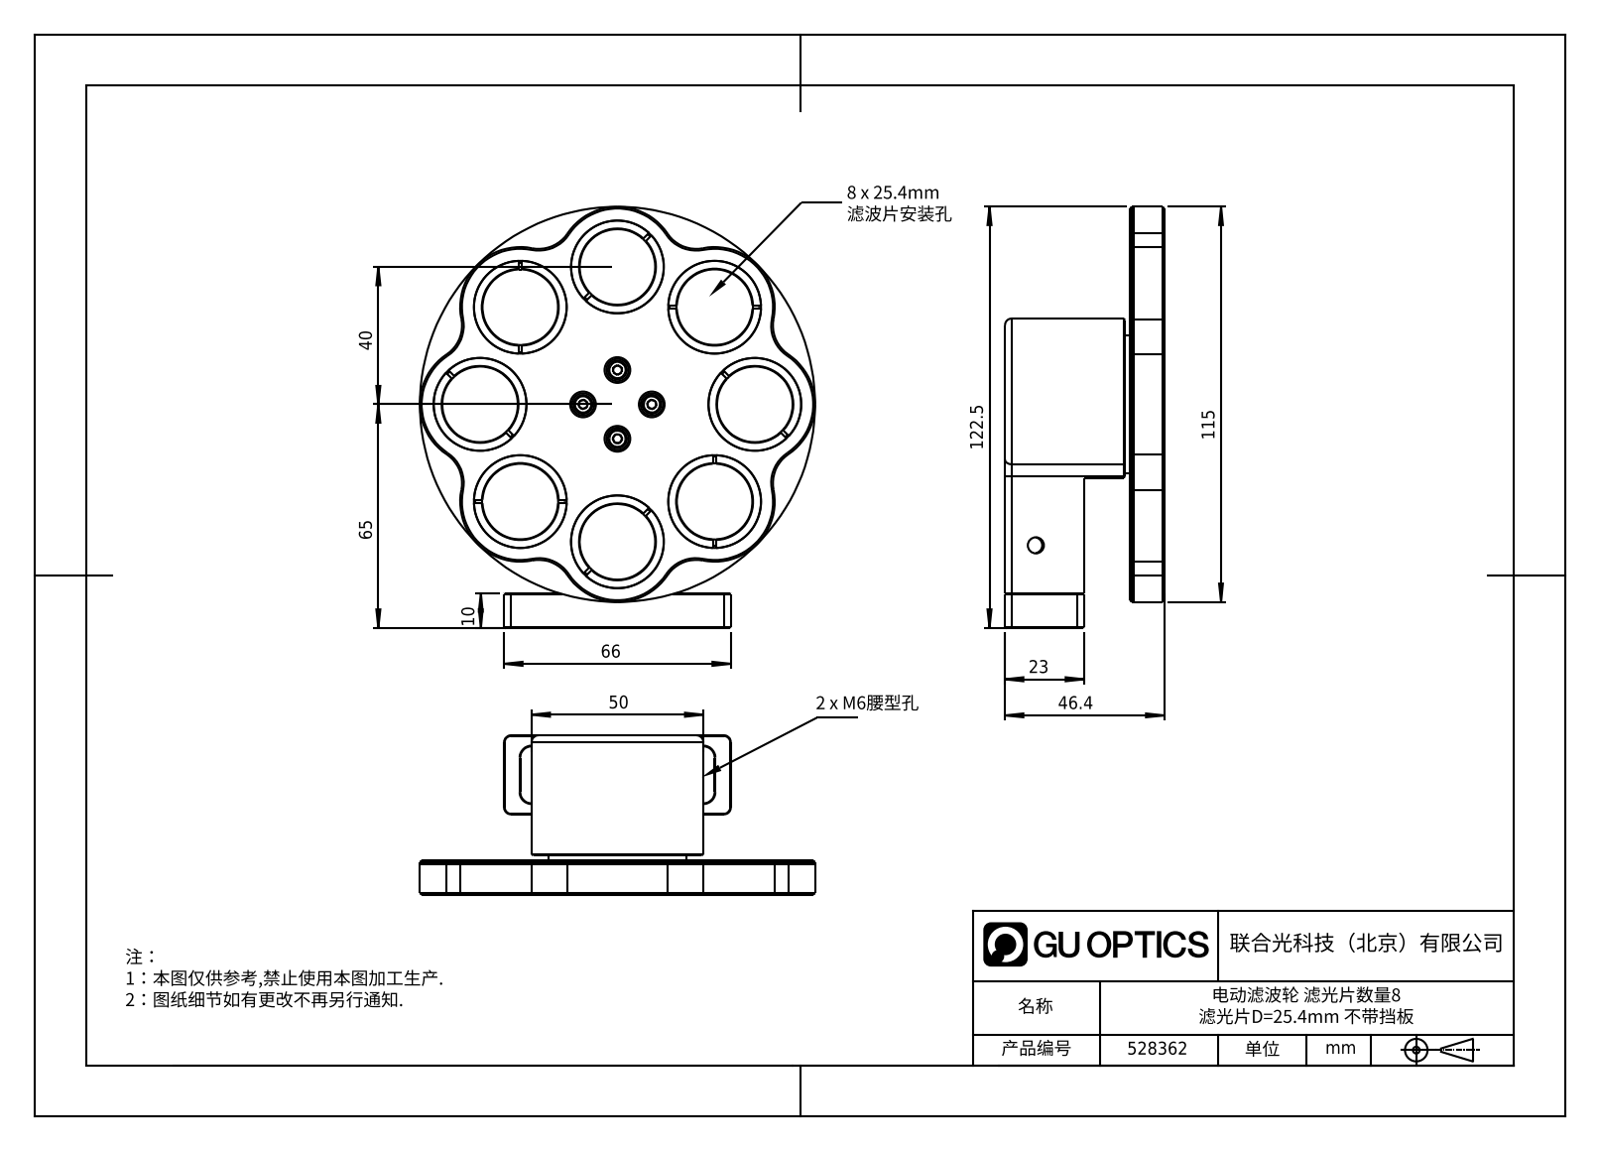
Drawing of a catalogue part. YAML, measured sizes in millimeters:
part_name: "528362"
step_written_by: "SolidWorks 2020 (CONFIG_CONTROL_DESIGN)"
units: millimeters
bodies: {solids: 0, faces: 464, planar: 263, cylindrical: 102, other: 99}
overall_size: [122.5, 115, 46.4]
round_holes:
  - {diameter: 27, count: 6}
  - {diameter: 8, count: 4}
  - {diameter: 4.7, count: 1}
  - {diameter: 115, count: 1}
round_bosses_or_shafts:
  - {diameter: 26, count: 8}
  - {diameter: 23, count: 8}
  - {diameter: 22, count: 8}
  - {diameter: 6.5, count: 4}
  - {diameter: 5.5, count: 4}
  - {diameter: 5.2, count: 4}
  - {diameter: 7, count: 2}
  - {diameter: 3.5, count: 2}
partial_cylinders:
  - {radius: 0.3, count: 20}
  - {radius: 10, count: 8}
  - {radius: 17.5, count: 8}
  - {radius: 2, count: 6}
  - {radius: 3.3, count: 4}
  - {radius: 5, count: 2}
  - {radius: 25, count: 1}
face_to_face_distances: [10, 1, 9, 6, 5, 4, 36.4, 37.4, 42.4, 46.4]
hole_center_spacings: [40, 30.61, 56.57, 73.91, 12, 27, 29.55, 39.99]
